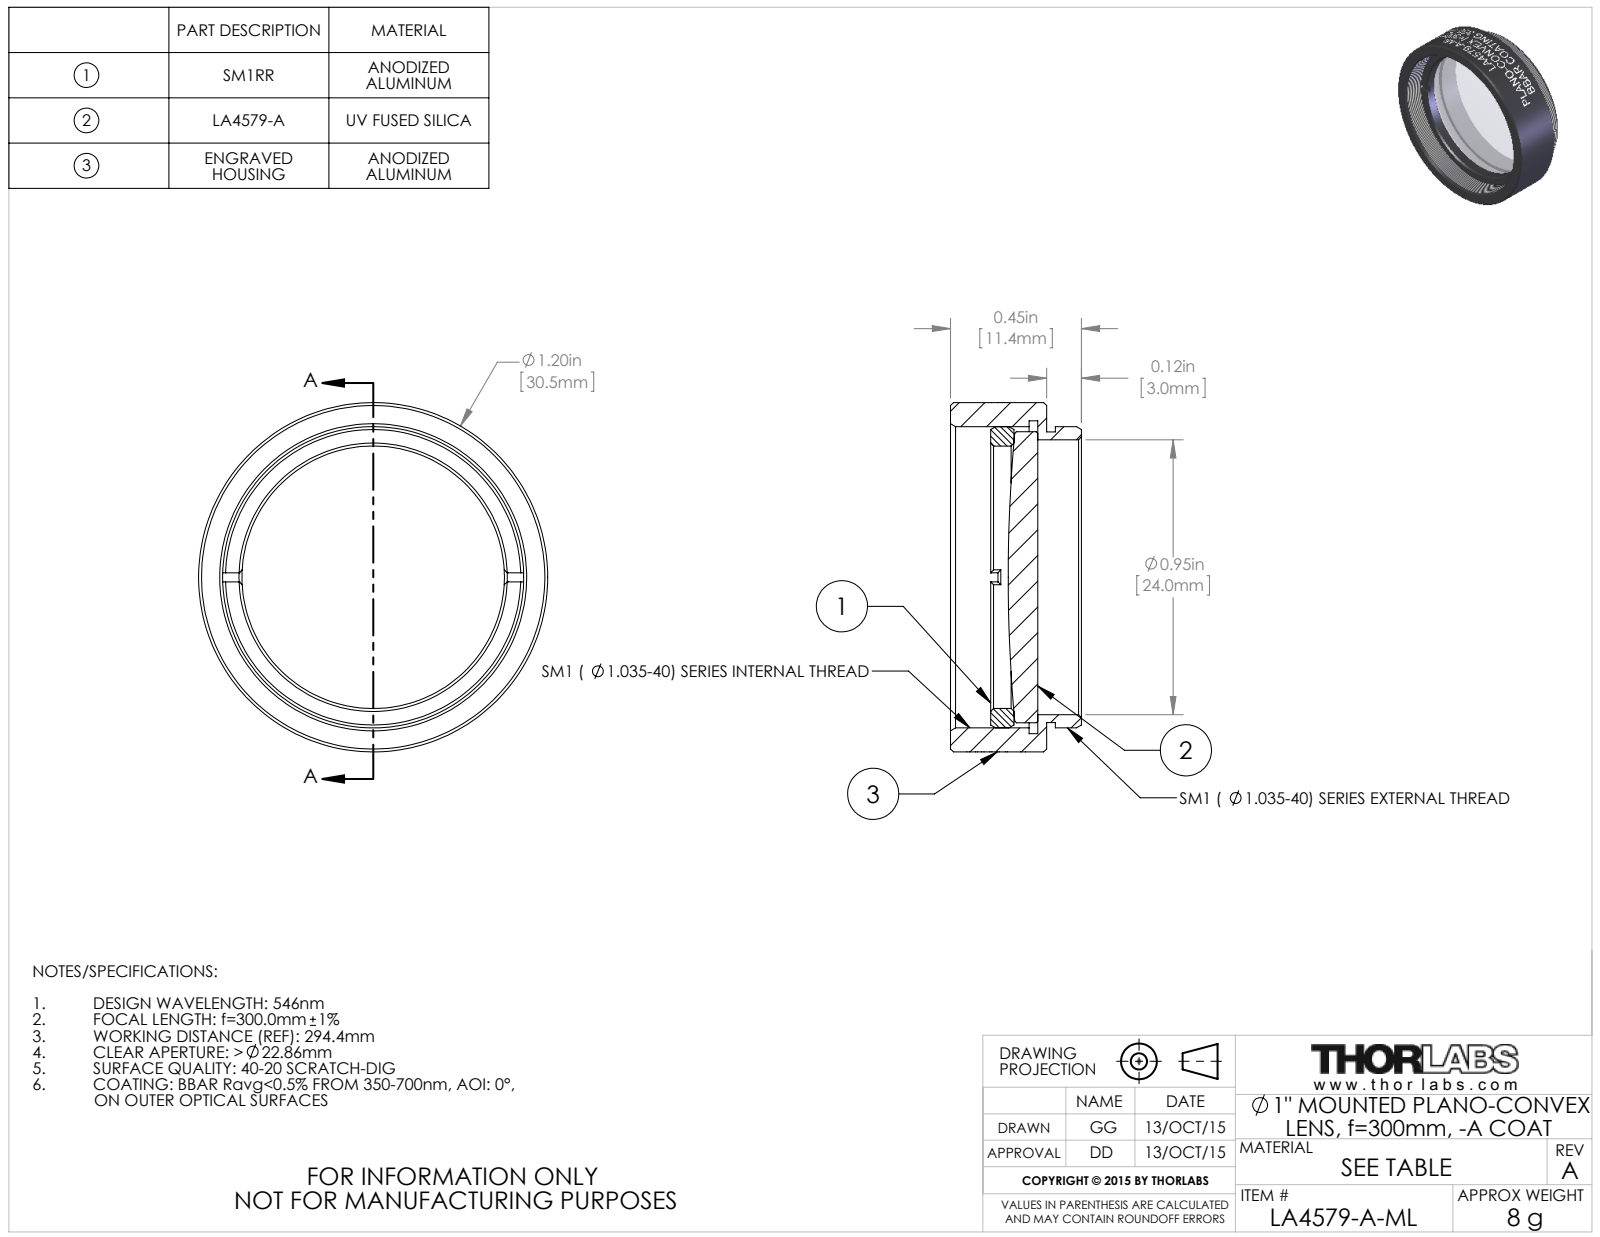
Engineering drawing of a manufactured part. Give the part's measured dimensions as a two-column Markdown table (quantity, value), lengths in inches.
| quantity | value |
| --- | --- |
| part name | TTN039312-E0W |
| STEP written by | SolidWorks 2014 (CONFIG_CONTROL_DESIGN) |
| units | inches |
| bodies | 3 solids, 161 faces (20 planar, 113 cylindrical, 28 other) |
| overall size | 1.2 × 1.2 × 0.45 |
| volume | 0.198 in³ |
| surface area | 6.667 in² |
| round holes (diameter × count) | 0.902 × 1, 0.945 × 1, 1.075 × 1 |
| round bosses / shafts (diameter × count) | 1.2 × 1, 1.035 × 1, 1 × 1, 0.999 × 1 |
| main face-to-face distances | 0.03, 0.33, 0.3, 0.137, 0.163, 0.112, 0.082, 0.218, 0.193, 0.08 |
